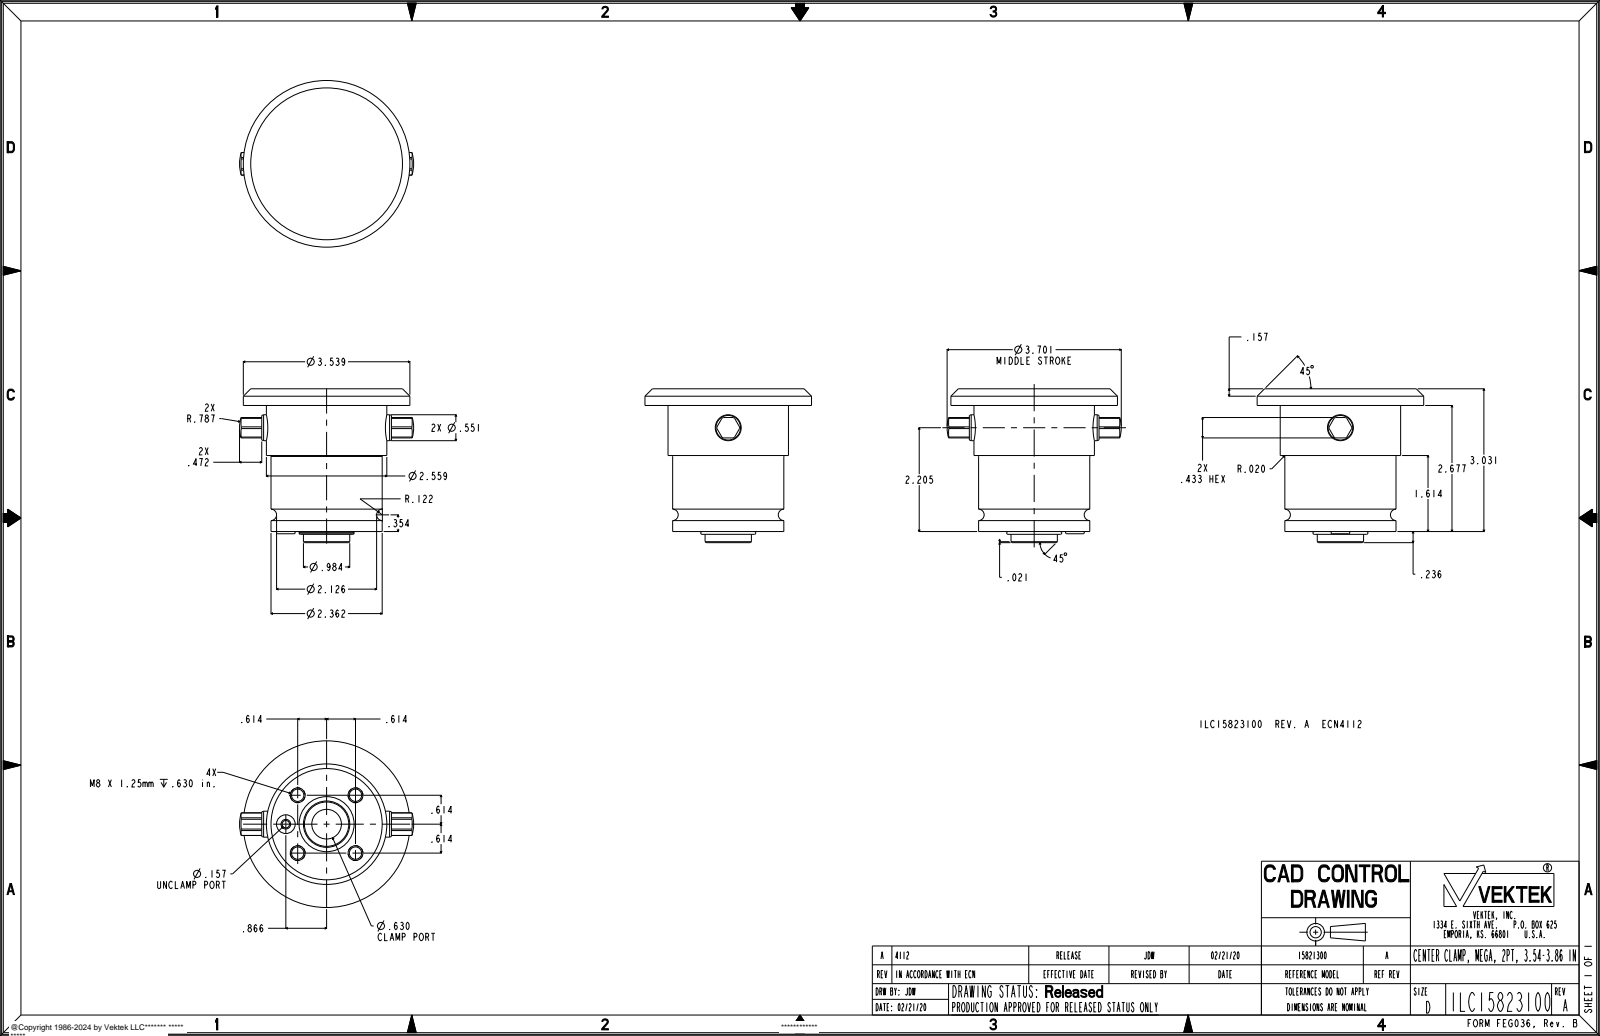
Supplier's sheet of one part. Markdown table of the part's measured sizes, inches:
| quantity | value |
| --- | --- |
| part name | ILC15823100 |
| STEP written by | PRO/ENGINEER BY PARAMETRIC TECHNOLOGY CORPORATION, 2013320 (AUTOMOTIVE_DESIGN) |
| units | inches |
| bodies | 1 solid, 135 faces (37 planar, 54 cylindrical, 44 other) |
| overall size | 3.701 × 3.539 × 3.268 |
| volume | 15.89 in³ |
| surface area | 53.29 in² |
| round holes (diameter × count) | 0.262 × 4, 0.157 × 1, 0.551 × 1, 0.63 × 1 |
| round bosses / shafts (diameter × count) | 0.315 × 4, 3.539 × 1, 2.559 × 1, 2.362 × 1, 1.169 × 1, 0.984 × 1 |
| partial cylindrical surfaces (radius × count) | 0.24 × 1 |
| main face-to-face distances | 0.354, 2.677, 3.031, 0.118, 1.614, 1.063, 1.417, 0.433, 0.098, 1.083 |
| hole center spacings | 0.869, 1.228, 0.664, 1.603, 1.737, 0.866 |
